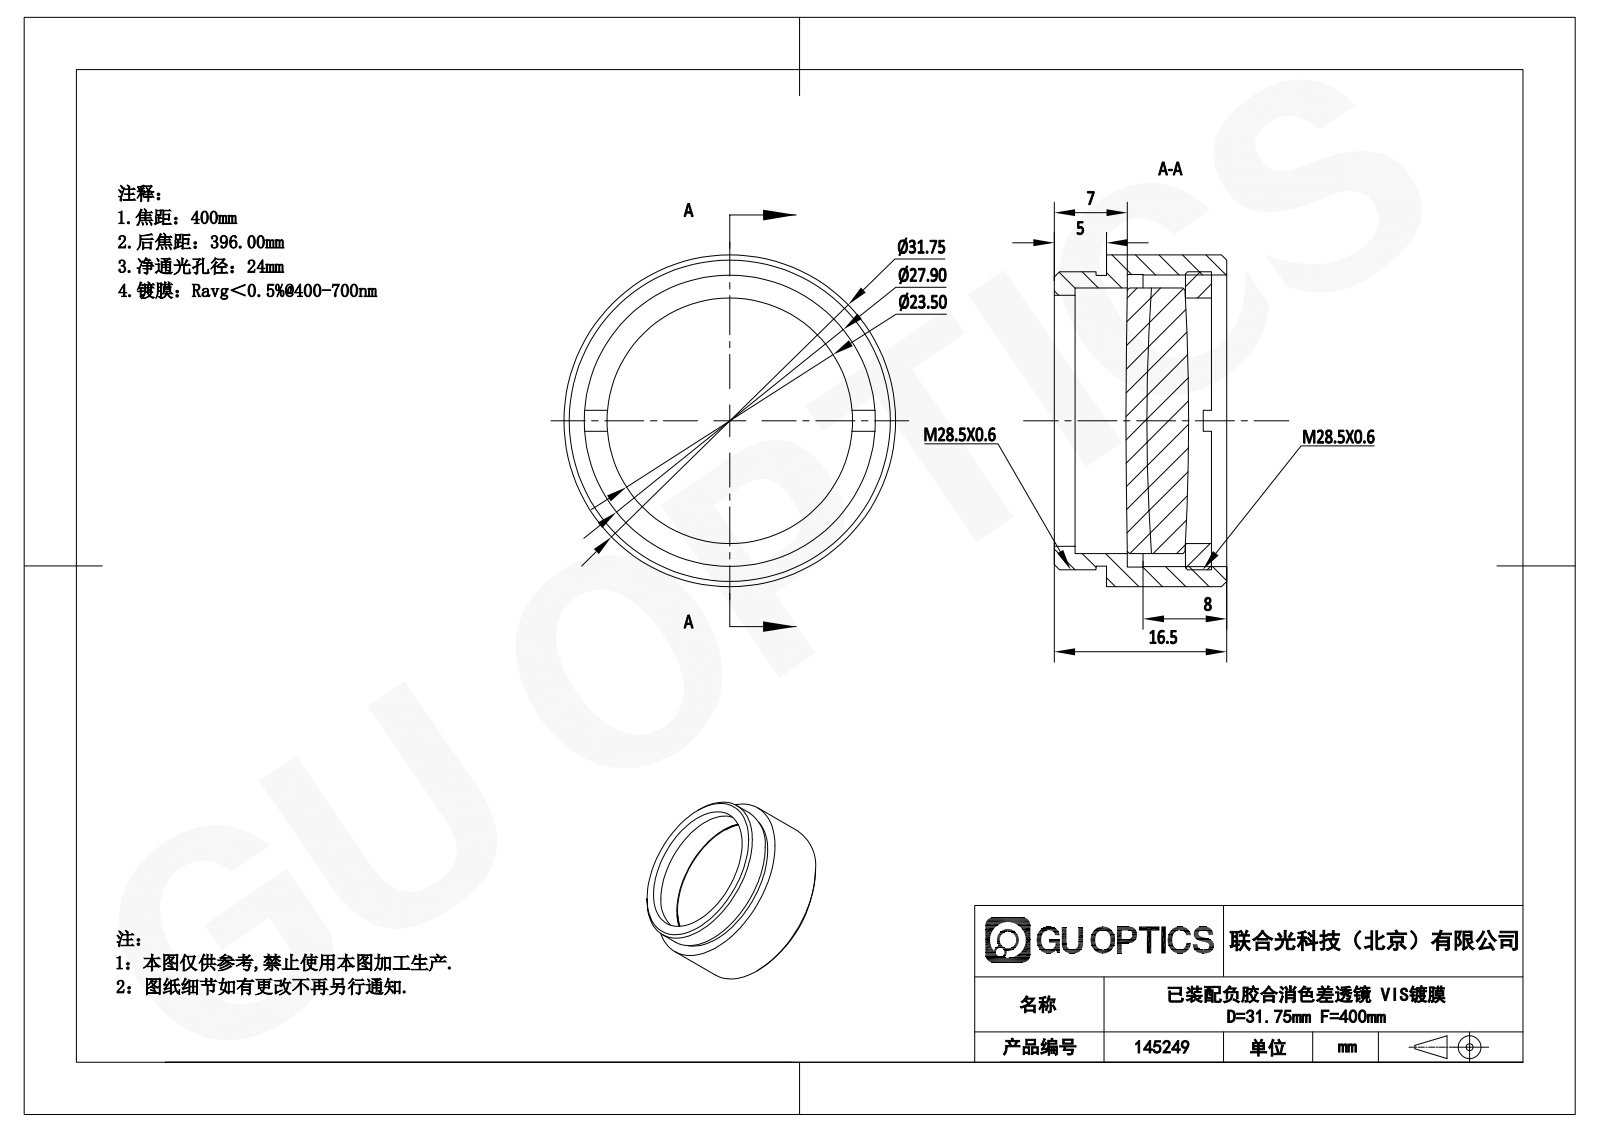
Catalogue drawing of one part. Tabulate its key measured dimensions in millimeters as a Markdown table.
| quantity | value |
| --- | --- |
| part name | M28.5x0.6ѹȦ; APD-ML25-400-VIS; GL31-025B-400-VIS_Solidworks |
| STEP written by | SolidWorks 2022 (AUTOMOTIVE_DESIGN) |
| units | millimeters |
| bodies | 4 solids, 56 faces (16 planar, 22 cylindrical, 18 other) |
| overall size | 31.76 × 31.76 × 16.5 |
| volume | 6 400 mm³ |
| surface area | 6 928 mm² |
| round holes (diameter × count) | 23.5 × 1, 24 × 1, 27.9 × 1, 28 × 1 |
| round bosses / shafts (diameter × count) | 31.76 × 1, 28.5 × 1, 27.8 × 1, 25.4 × 1 |
| main face-to-face distances | 2, 5, 2.5, 7.55, 10.05, 12.55, 15.05, 16.5, 11.5, 3.95 |
